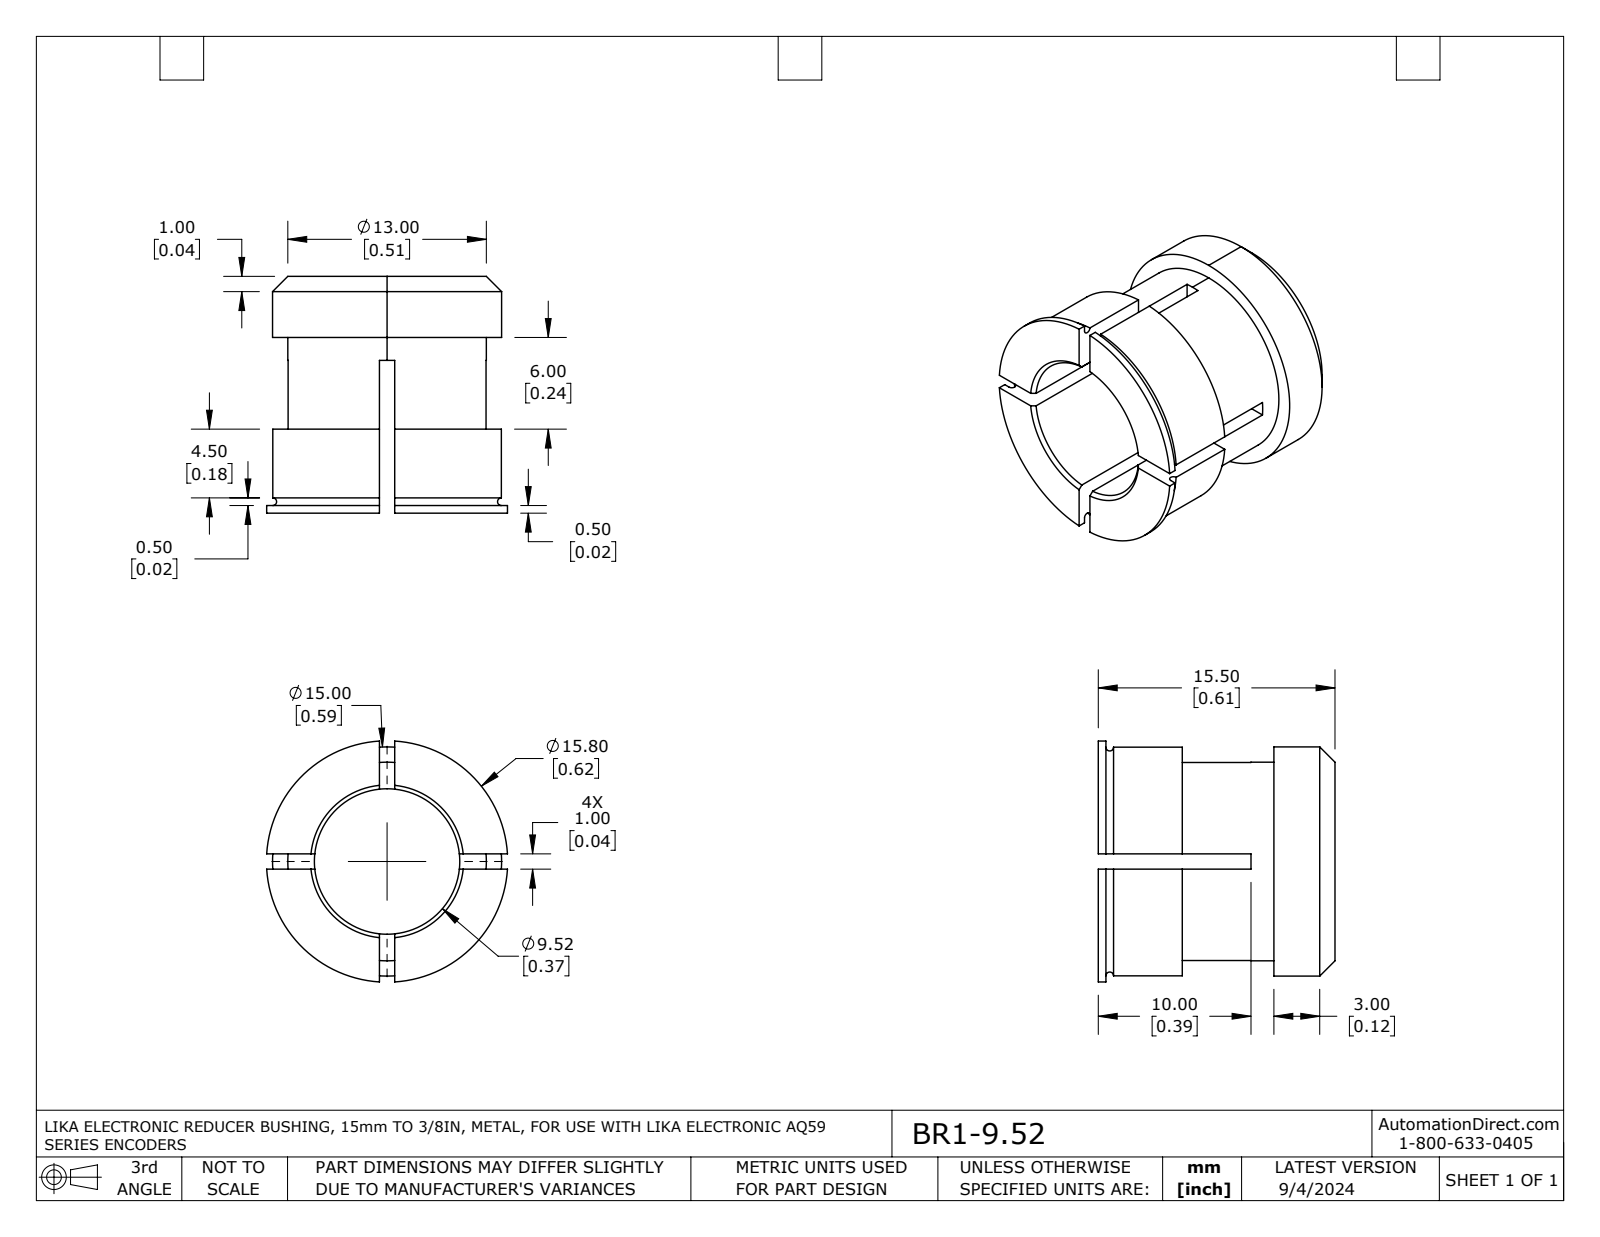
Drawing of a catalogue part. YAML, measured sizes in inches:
part_name: "BR1-9.52"
step_written_by: "SolidWorks 2021 (AUTOMOTIVE_DESIGN)"
units: inches
bodies: {solids: 1, faces: 54, planar: 26, cylindrical: 17, other: 11}
overall_size: [0.621, 0.621, 0.61]
volume: 0.077
surface_area: 2.429
round_holes:
  - {diameter: 0.375, count: 1}
round_bosses_or_shafts:
  - {diameter: 0.622, count: 1}
  - {diameter: 0.591, count: 1}
  - {diameter: 0.512, count: 1}
face_to_face_distances: [0.039, 0.61, 0.217, 0.394, 0.157, 0.453, 0.236, 0.591, 0.433, 0.197]
